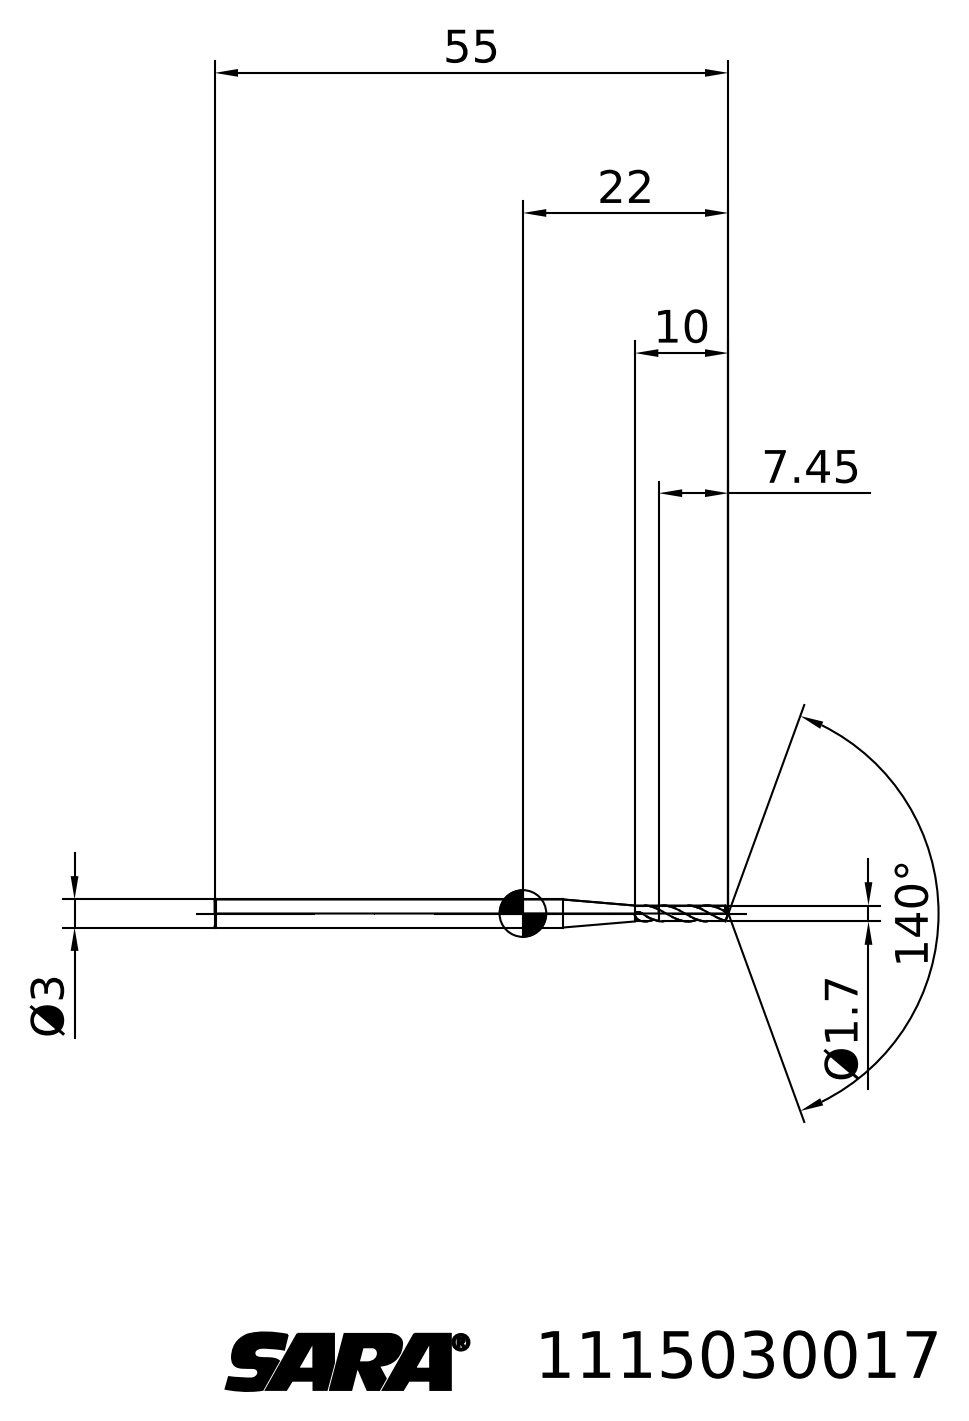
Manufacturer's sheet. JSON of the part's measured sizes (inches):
{"step_written_by": "TDM (AUTOMOTIVE_DESIGN)", "units": "inches", "bodies": {"solids": 2, "faces": 26, "planar": 3, "cylindrical": 0, "other": 23}, "overall_size": [2.165, 0.118, 0.118], "volume_in3": 0.019, "surface_area_in2": 0.738, "face_to_face_distances": [1.872]}
